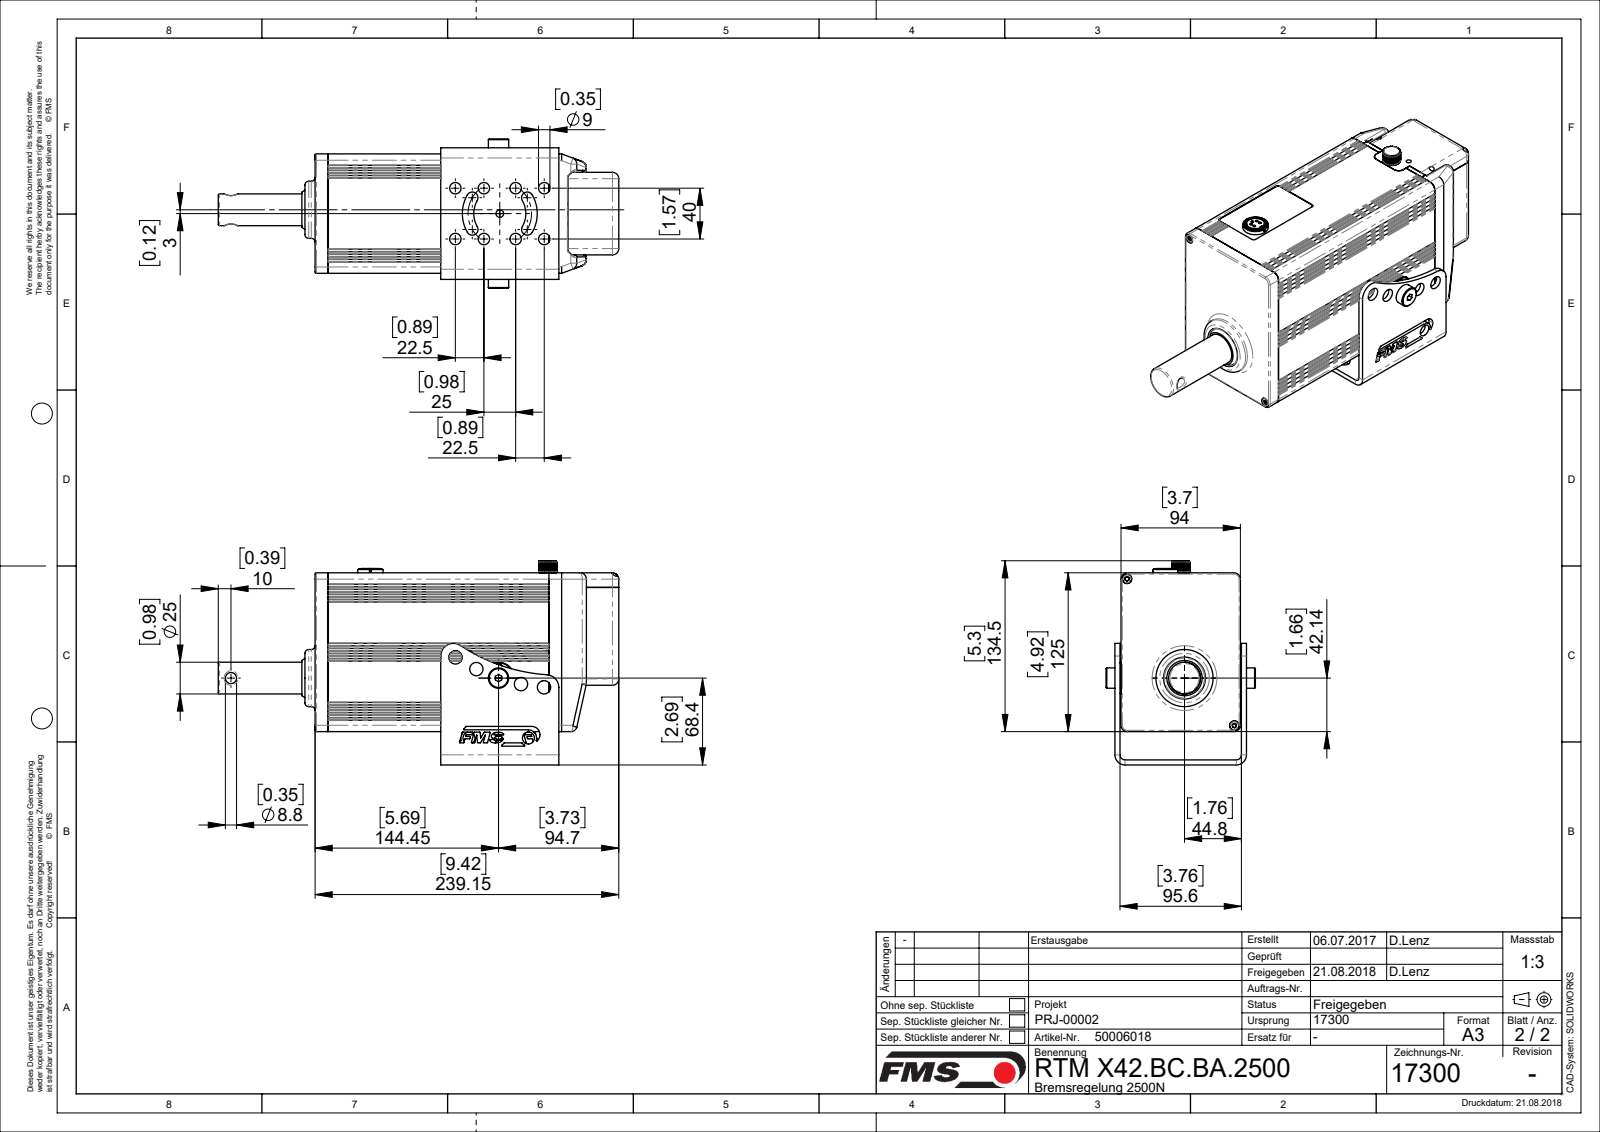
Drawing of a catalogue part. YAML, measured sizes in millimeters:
part_name: "ZEICHNUNG1; 17300; 17880_STANDART; 17827 (+8 more)"
step_written_by: "Mechanical Desktop 2009 (CONFIG_CONTROL_DESIGN)"
units: millimeters
bodies: {solids: 18, faces: 2030, planar: 672, cylindrical: 921, other: 437}
overall_size: [289.89, 154.66, 117.6]
volume: 660159
surface_area: 365000
round_holes:
  - {diameter: 4.5, count: 8}
  - {diameter: 9, count: 8}
  - {diameter: 3.3, count: 6}
  - {diameter: 7.5, count: 6}
  - {diameter: 1.6, count: 5}
  - {diameter: 10.5, count: 5}
  - {diameter: 2.62, count: 4}
  - {diameter: 3.7, count: 4}
  - {diameter: 2.7, count: 2}
  - {diameter: 4.2, count: 2}
  - {diameter: 5, count: 2}
  - {diameter: 5.5, count: 2}
round_bosses_or_shafts:
  - {diameter: 1.1, count: 5}
  - {diameter: 2.4, count: 4}
  - {diameter: 2, count: 4}
  - {diameter: 1.3, count: 4}
  - {diameter: 45, count: 1}
  - {diameter: 43, count: 1}
  - {diameter: 20, count: 1}
  - {diameter: 18, count: 1}
partial_cylinders:
  - {radius: 0.5, count: 176}
  - {radius: 0.3, count: 146}
  - {radius: 0.4, count: 56}
  - {radius: 1, count: 33}
  - {radius: 5, count: 33}
  - {radius: 0.2, count: 22}
  - {radius: 2, count: 20}
  - {radius: 2.5, count: 10}
face_to_face_distances: [3, 91, 4, 122, 88, 2.5, 0.5, 94, 91.8, 3.8]
hole_center_spacings: [22.5, 23.58, 40, 40.31, 45.89, 47.5, 62.1, 3.49]
